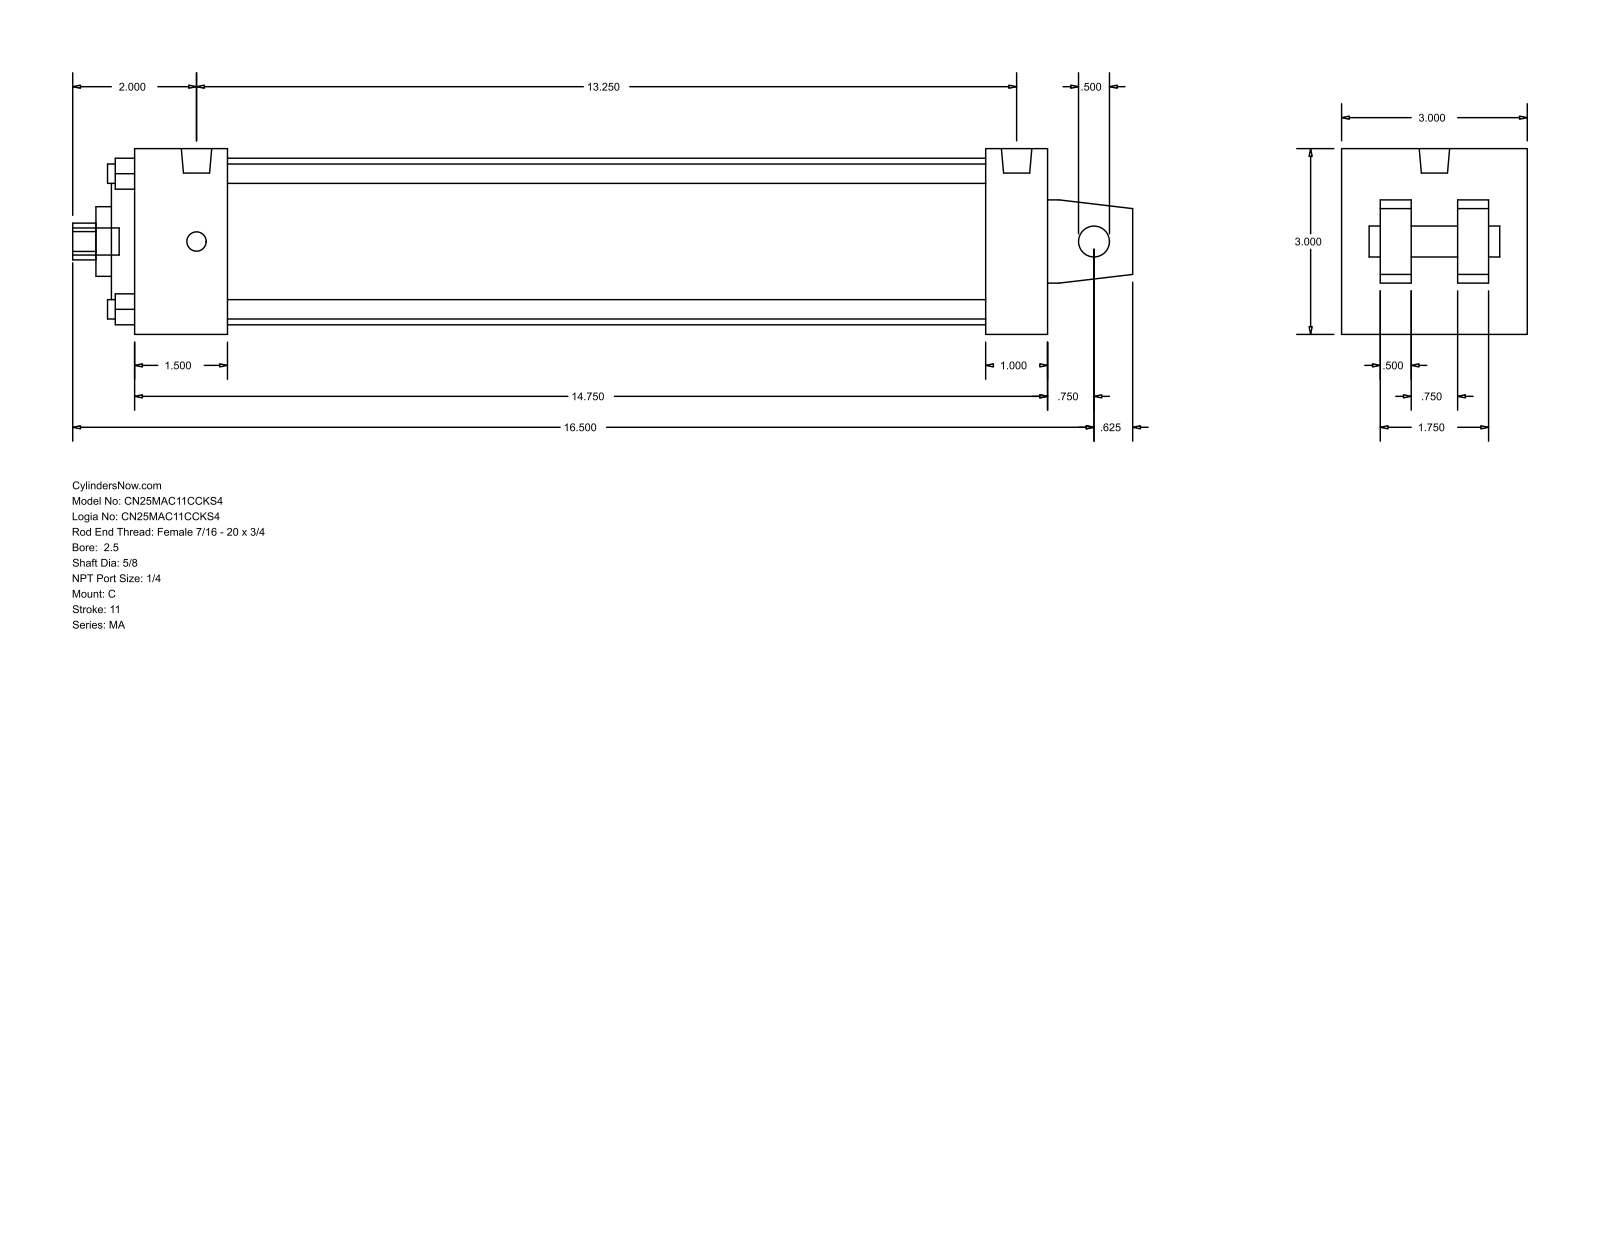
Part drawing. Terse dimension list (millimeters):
name: MA_C__0250_0.625
written by: GSSL Pune (CONFIG_CONTROL_DESIGN)
unit: mm
bodies: 0 solids, 105 faces (77 planar, 28 cylindrical, 0 other)
size: 434.98 × 76.2 × 76.2
holes: 4× ⌀7.94, 1× ⌀12.7, 1× ⌀15.88, 1× ⌀28.57, 1× ⌀50.8, 1× ⌀68.33
bosses: 4× ⌀7.94, 2× ⌀12.49, 1× ⌀11.11
rounds: 1× R7.54
face distances: 76.2, 374.65, 12.7, 15.87, 60.33, 47.63, 25.4, 38.1, 349.25, 311.15
hole spacings: 39.33, 55.62, 78.66
